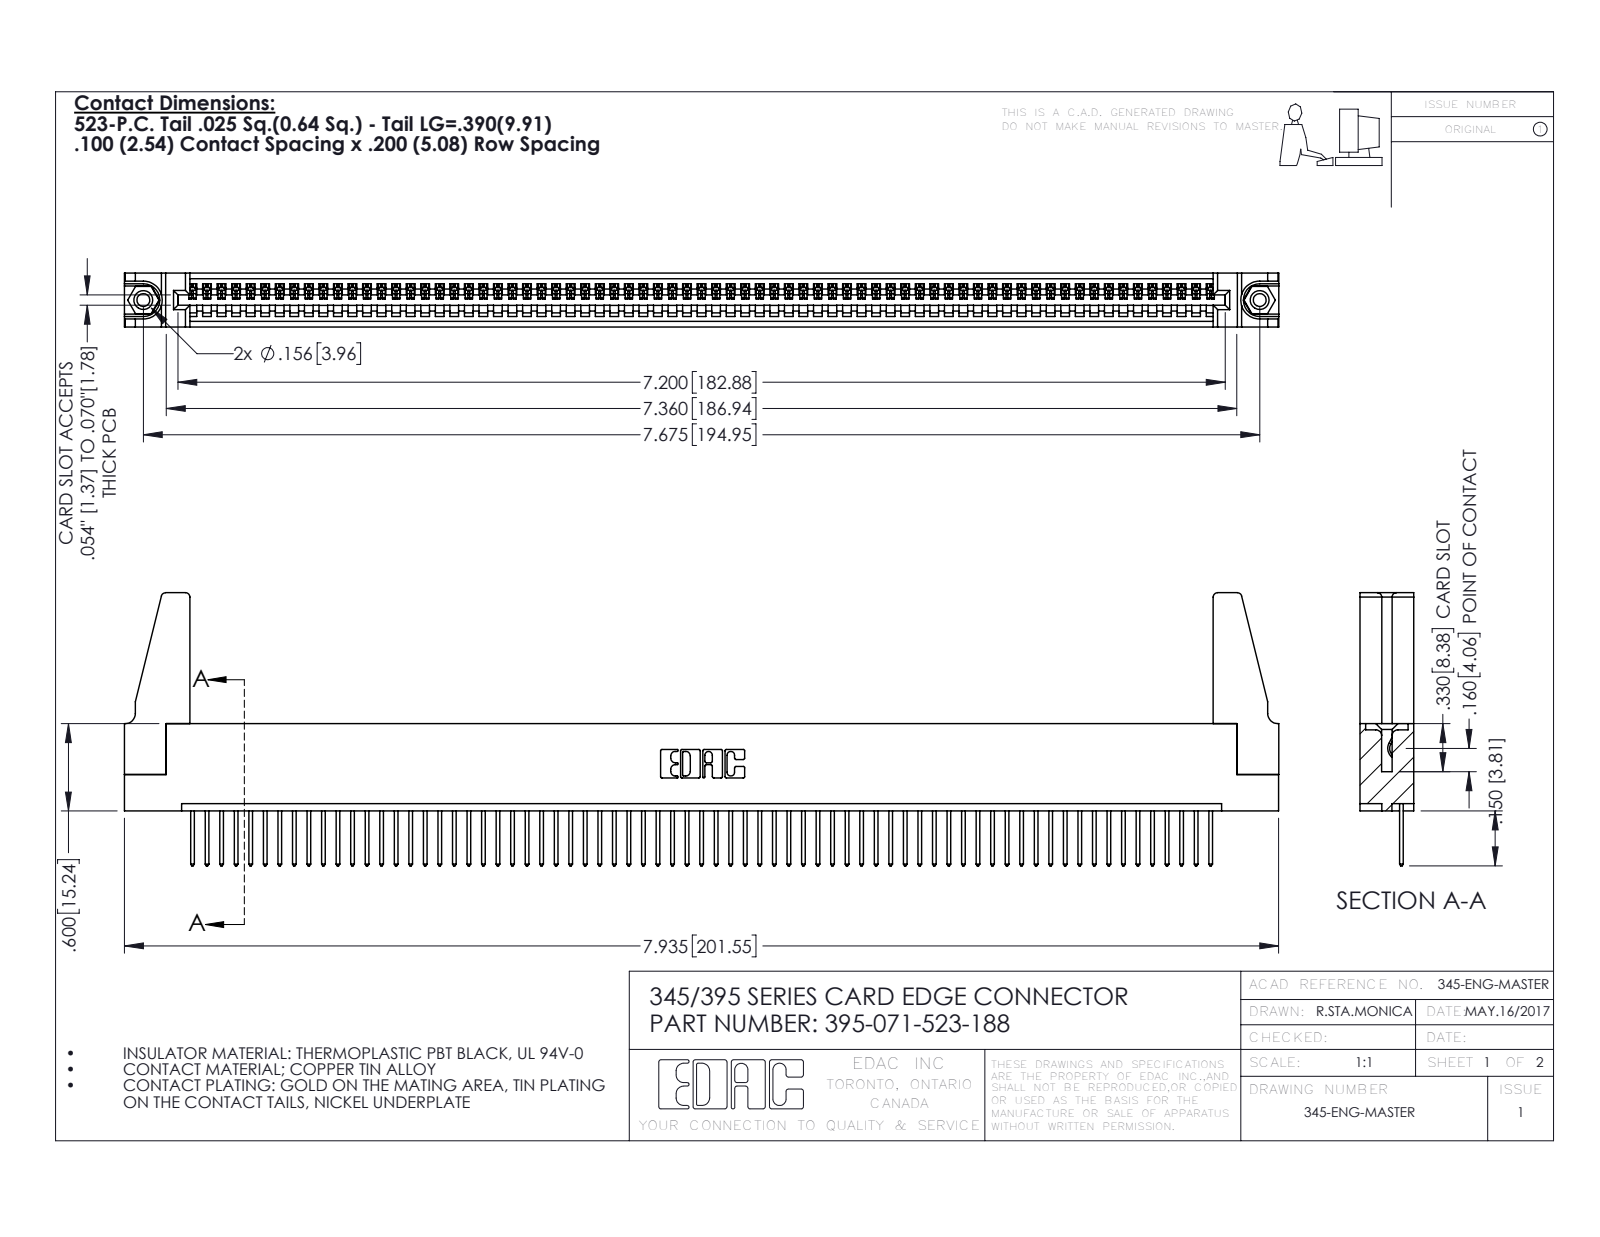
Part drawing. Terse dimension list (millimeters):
name: 345-220-078_345-220-088; 345-292-001_345-293-123; 345 Part_Flush Mounting Lugs - 0.156 Dia-TH; 395-071-523-188 (+1 more)
written by: SolidWorks 2016 (CONFIG_CONTROL_DESIGN)
unit: mm
bodies: 76 solids, 4368 faces (2992 planar, 1360 cylindrical, 16 other)
size: 201.6 × 47.7 × 9.4
volume: 22 610 mm³; area: 29 320 mm²
holes: 2× ⌀2.3, 2× ⌀3.2, 2× ⌀4, 1× ⌀1.6
bosses: 2× ⌀3.9
rounds: 142× R0.2, 142× R0.3, 22× R0.3, 8× R0.8, 6× R0.2, 6× R0.8, 3× R0.7, 2× R0.8
face distances: 1.8, 7.6, 9.4, 5.1, 2.5, 6.9, 0.6, 5.7, 3.8, 1.8
hole spacings: 6.9, 189, 194.9
